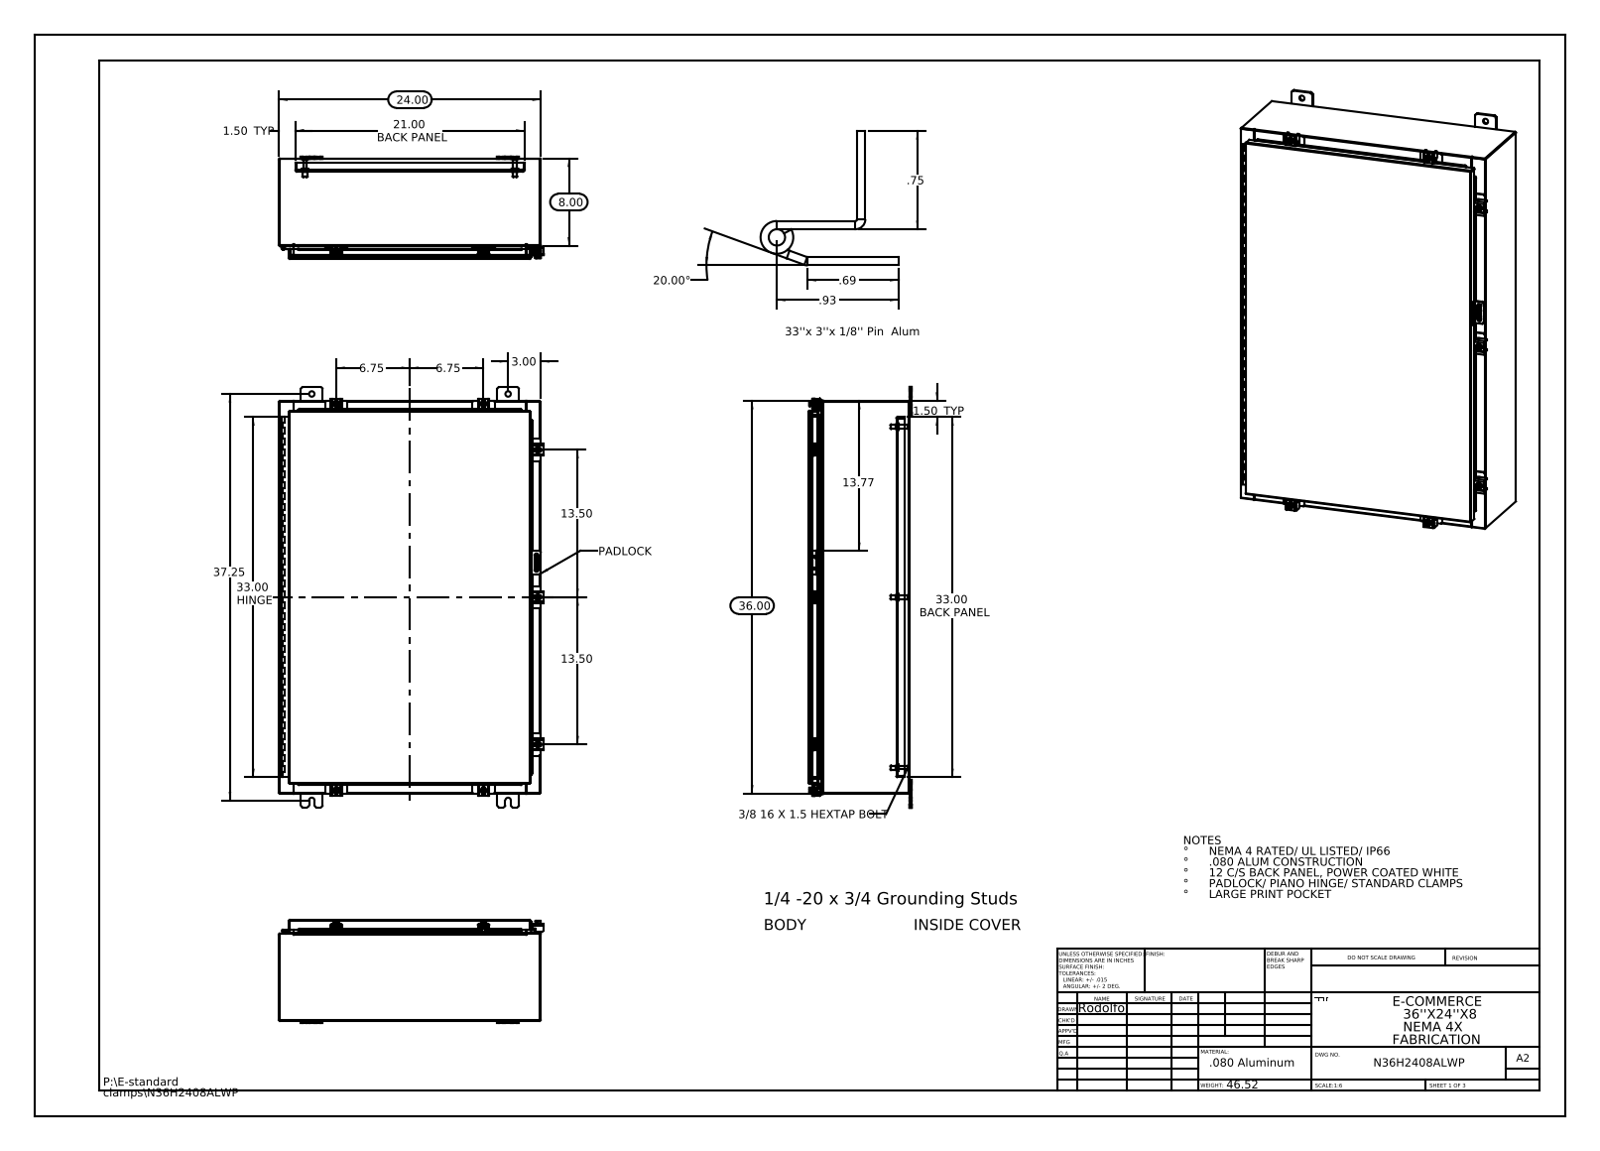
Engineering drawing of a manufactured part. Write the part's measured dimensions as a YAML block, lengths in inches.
part_name: "N36H2408ALWP Backpanel; N36H2408ALWP Bottom; N36H2408ALWP Clamp Assembly; N36H2408ALWP Hinge Enclosure Side2 (+8 more)"
step_written_by: "SolidWorks 2013 (CONFIG_CONTROL_DESIGN)"
units: inches
bodies: {solids: 54, faces: 2184, planar: 1138, cylindrical: 922, other: 124}
overall_size: [38.5, 24.211, 9.389]
volume: 310.6
surface_area: 7747
round_holes:
  - {diameter: 0.5, count: 10}
  - {diameter: 0.213, count: 7}
  - {diameter: 0.26, count: 7}
  - {diameter: 0.125, count: 2}
  - {diameter: 0.125, count: 1}
round_bosses_or_shafts:
  - {diameter: 0.25, count: 8}
  - {diameter: 0.5, count: 7}
  - {diameter: 0.399, count: 7}
  - {diameter: 0.625, count: 6}
  - {diameter: 0.375, count: 6}
  - {diameter: 0.33, count: 6}
partial_cylinders:
  - {radius: 0.06, count: 34}
  - {radius: 0.013, count: 27}
  - {radius: 0.19, count: 24}
  - {radius: 0.088, count: 21}
  - {radius: 0.12, count: 14}
  - {radius: 0.141, count: 14}
  - {radius: 0.05, count: 11}
  - {radius: 0.08, count: 10}
face_to_face_distances: [0.075, 9.126, 9.201, 9.051, 0.104, 1, 1.075, 8.051, 8.126, 1.179]
hole_center_spacings: [13.5, 15.625, 17.957, 24.793, 33.474, 37.154, 19.25, 1.858]
